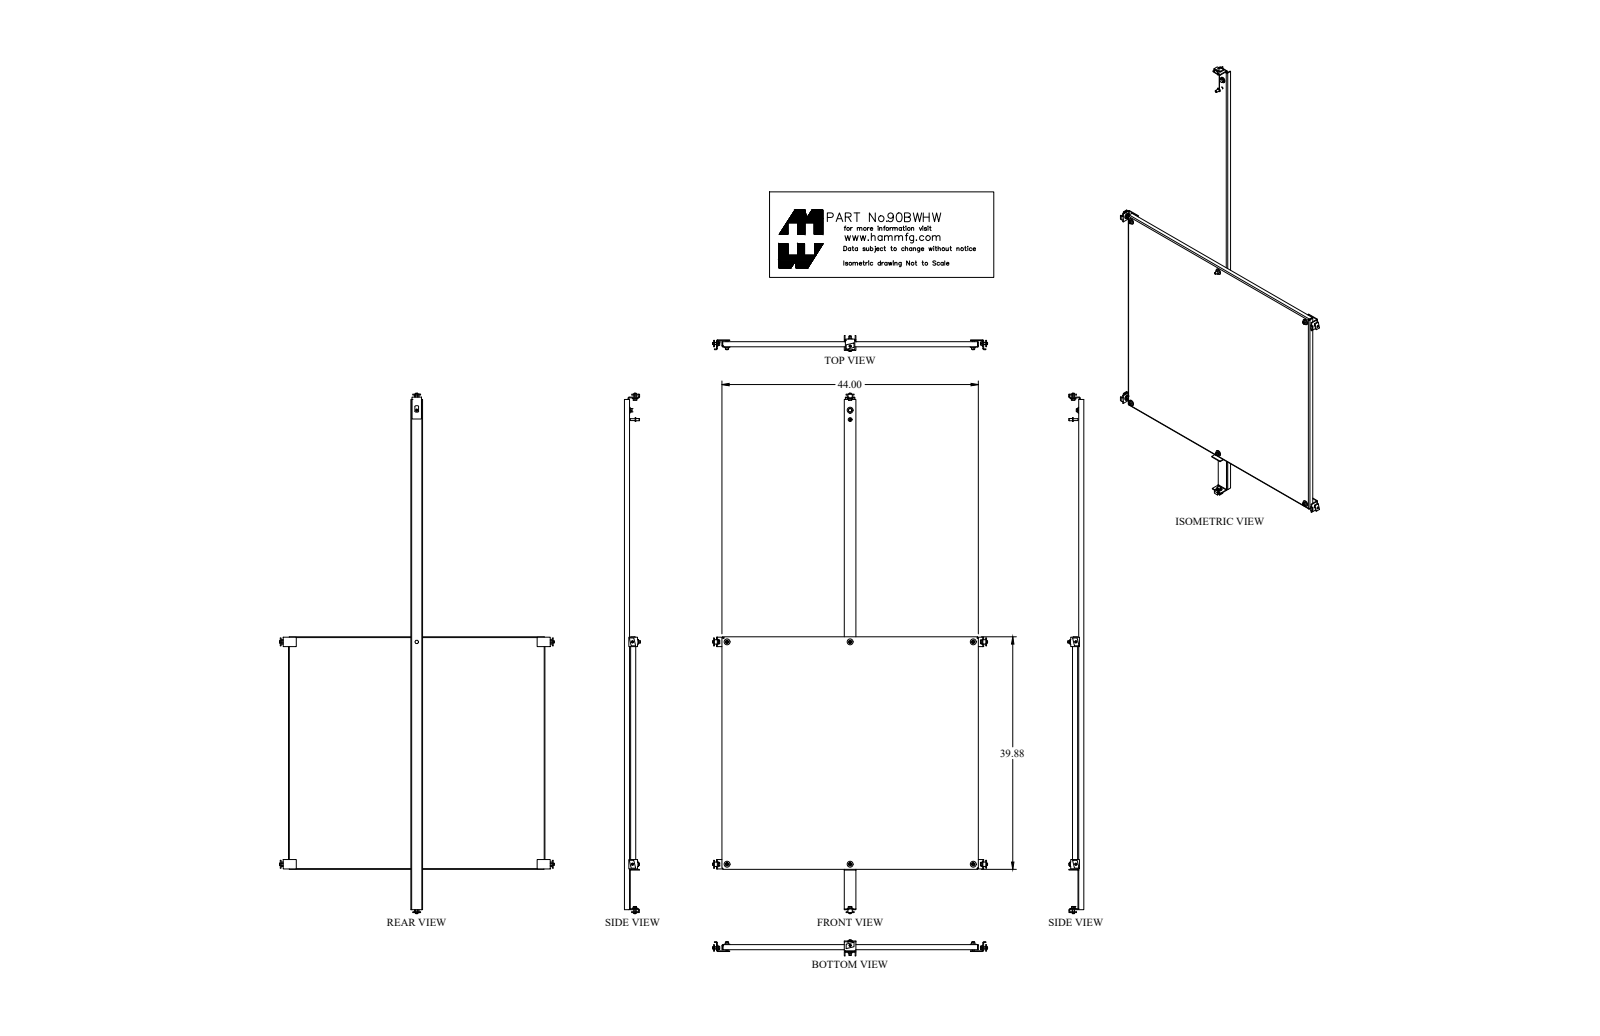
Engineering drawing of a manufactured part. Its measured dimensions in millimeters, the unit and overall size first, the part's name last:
Units: millimetres
Overall size (bounding box): 1981.2 × 1117.6 × 22.2
Round holes (diameter × count): ⌀14.3 ×8
Partial cylindrical surfaces — rounded edges, fillets, slot ends (radius × count): R1.5 ×4, R4.7 ×4
Main face-to-face distances: 3.2, 1114.4, 3.2, 1978, 1117.6, 1111.3, 1974.9, 22.2, 19.1, 1981.2
Hole centre spacings: 536.6, 968.4, 1107.1, 1445.5, 2009.7, 1073.2, 1936.8, 2214.2
Volume: 7 373 000 mm³ · Surface area: 4 666 000 mm²
Bodies: 1 solid, 70 faces (38 planar, 24 cylindrical, 8 other)
Part name (STEP PRODUCT): 90BWHW_Default
STEP written by: SolidWorks 2018 (CONFIG_CONTROL_DESIGN)
